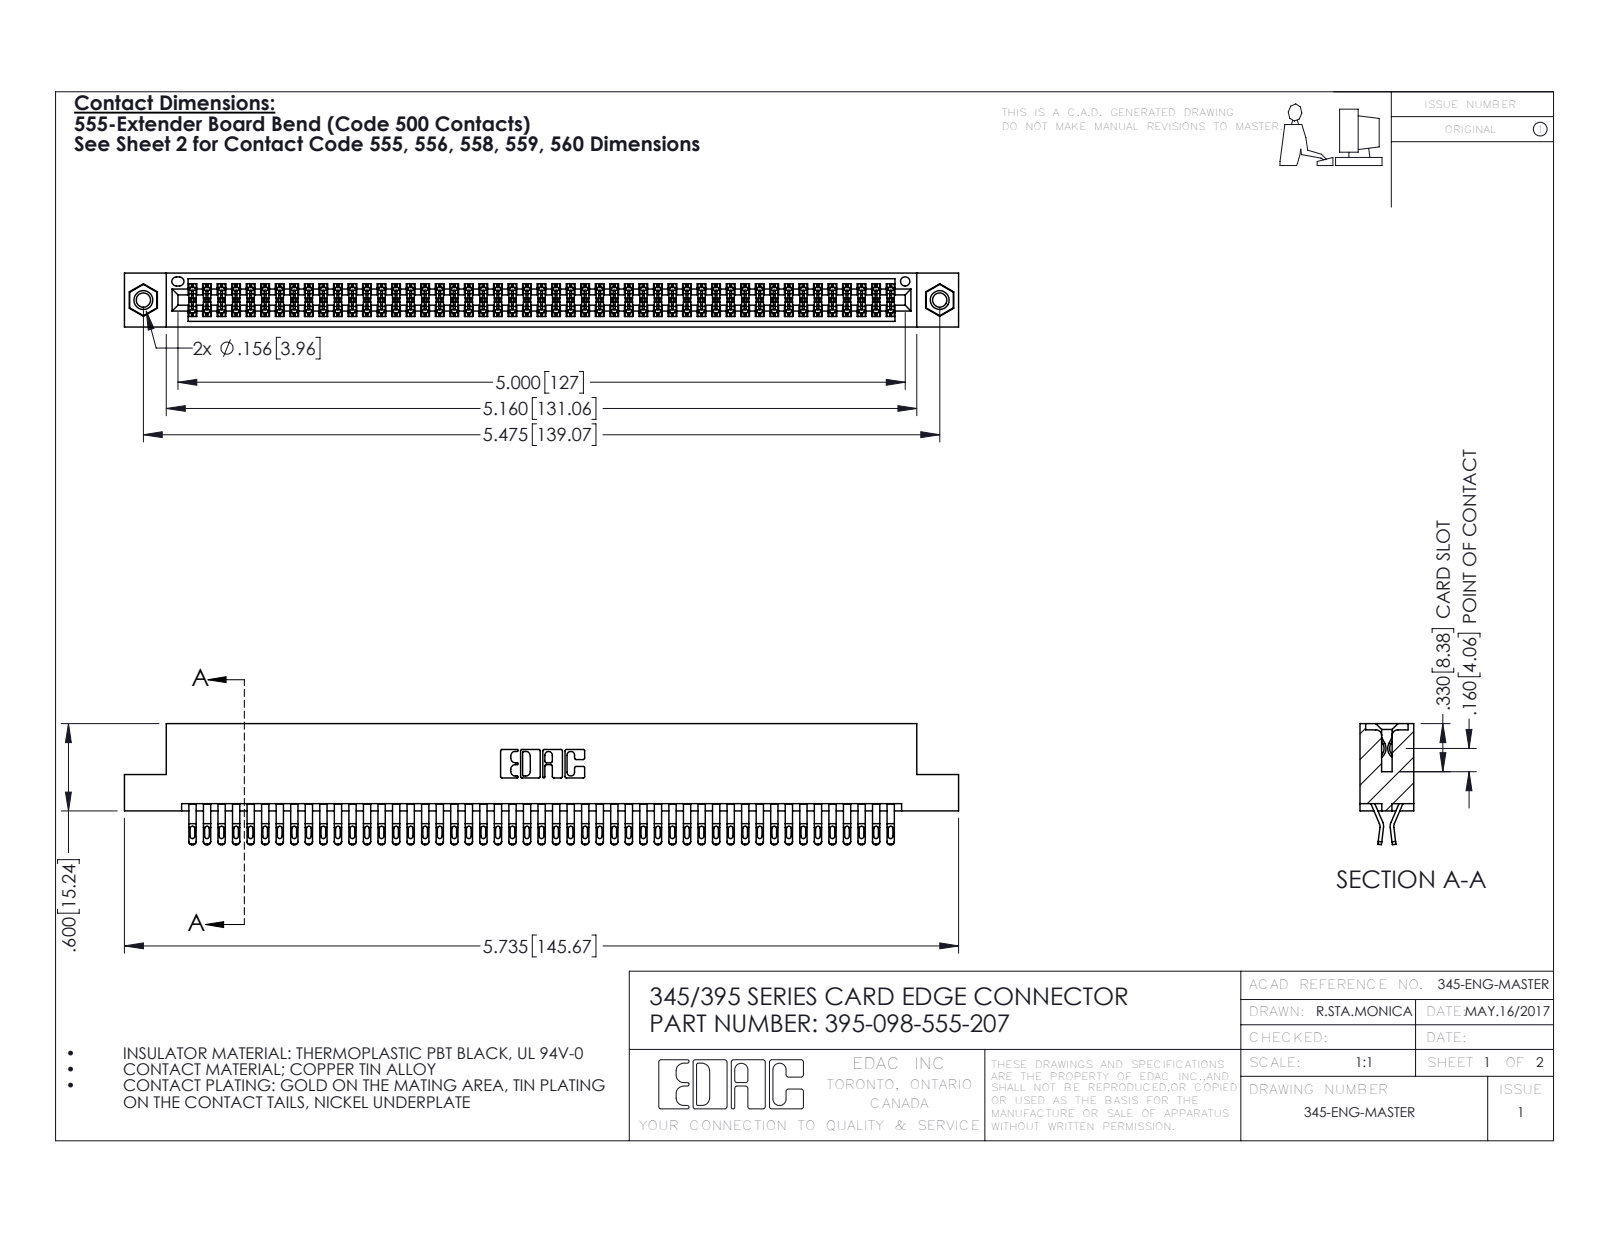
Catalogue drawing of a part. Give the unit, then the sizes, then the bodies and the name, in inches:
Units: inches
Overall size (bounding box): 5.735 × 0.832 × 0.37
Round holes (diameter × count): ⌀0.098 ×2, ⌀0.125 ×2, ⌀0.156 ×2, ⌀0.064 ×1
Round bosses / shafts (diameter × count): ⌀0.155 ×2
Partial cylindrical surfaces — rounded edges, fillets, slot ends (radius × count): R0.016 ×245, R0.02 ×196, R0.006 ×147, R0.01 ×22, R0.007 ×6, R0.031 ×6, R0.026 ×3, R0.01 ×2
Main face-to-face distances: 0.072, 0.298, 0.025, 0.2, 0.37, 0.098, 0.272, 0.225, 0.175, 0.149
Hole centre spacings: 0.27, 5.239, 5.475
Volume: 0.884 in³ · Surface area: 34.98 in²
Bodies: 101 solids, 5674 faces (3150 planar, 2508 cylindrical, 16 other)
Part name (STEP PRODUCT): 345-292-001_555 Tail; 395-098-555-207; 345-250-001_345-250-005-103; 345 Part_Flush Mounting Lugs - 0.156 Dia-TI
STEP written by: SolidWorks 2016 (CONFIG_CONTROL_DESIGN)
